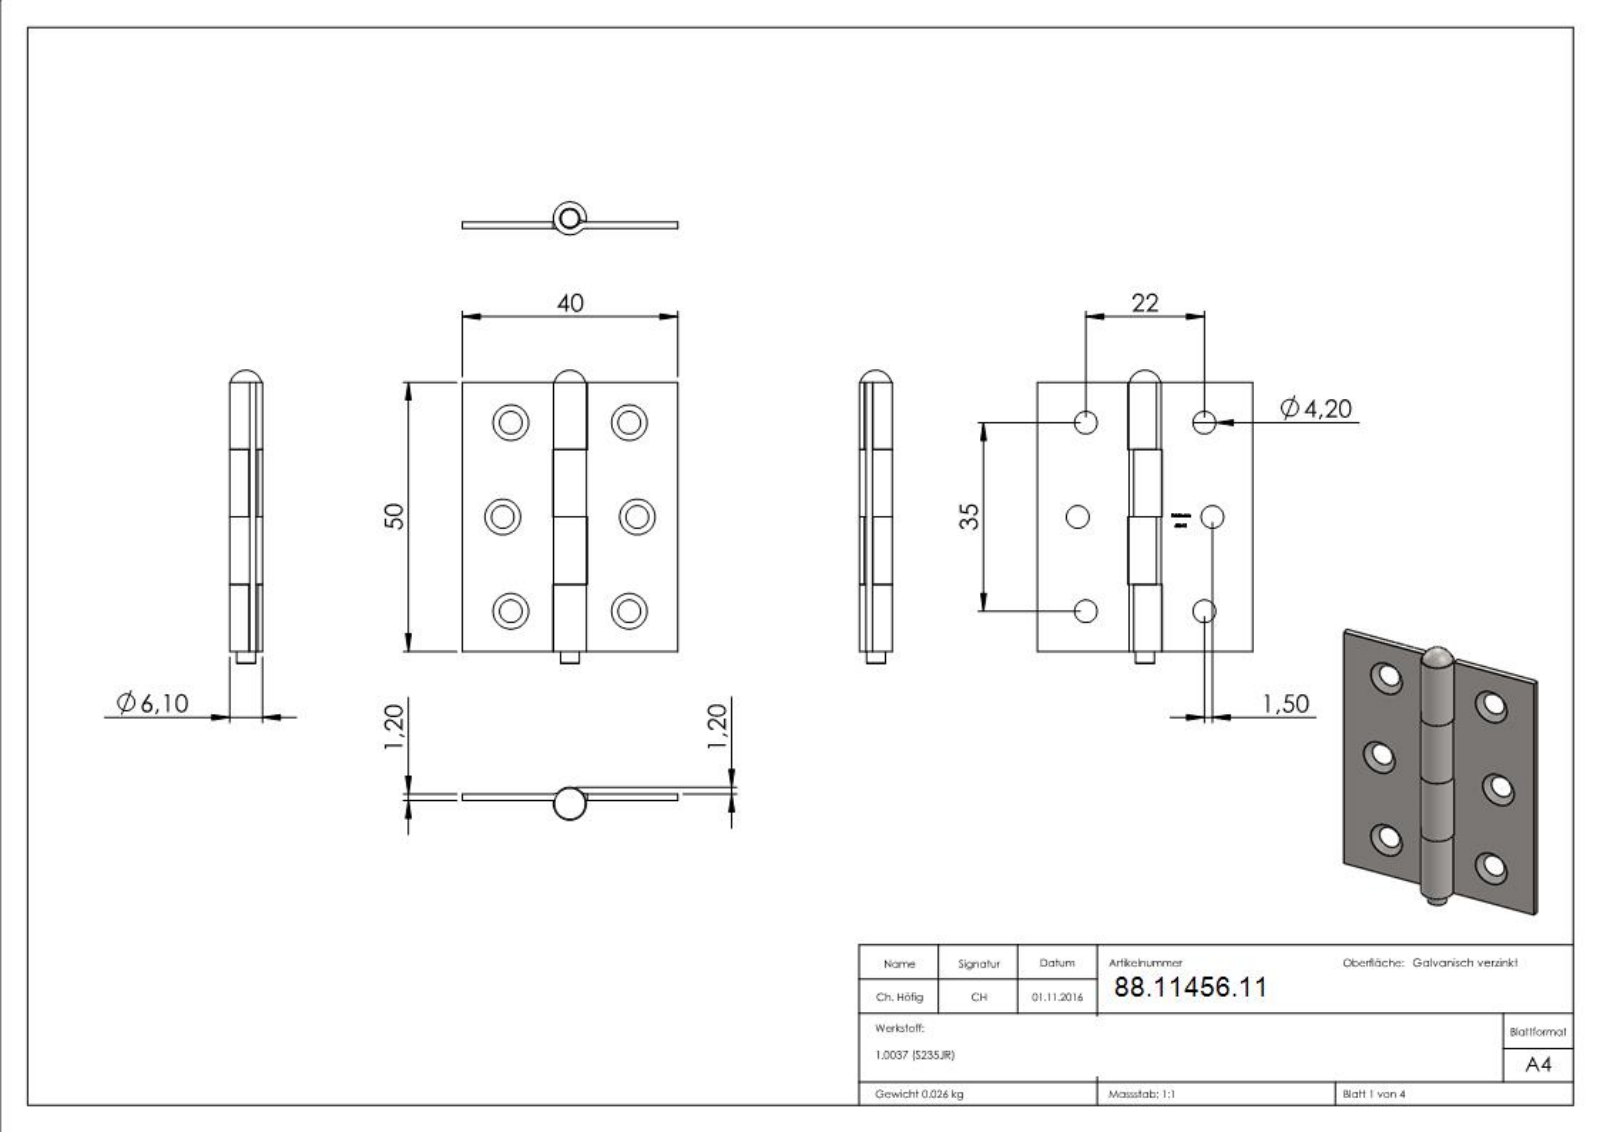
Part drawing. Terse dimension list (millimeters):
name: 456-11 Teil3; 456-11 Teil1; 456-11; 456-11 Teil2
written by: SolidWorks 2018 (CONFIG_CONTROL_DESIGN)
unit: mm
bodies: 3 solids, 227 faces (137 planar, 17 cylindrical, 73 other)
size: 54.4 × 40 × 6.1
volume: 3 315 mm³; area: 5 908 mm²
holes: 1× ⌀3.7
bosses: 1× ⌀6.1, 1× ⌀3.5
rounds: 2× R1.2, 2× R2.4
face distances: 1.2, 12.5, 25, 37.5, 16.8, 23.2, 40, 50, 6.4, 2.2
